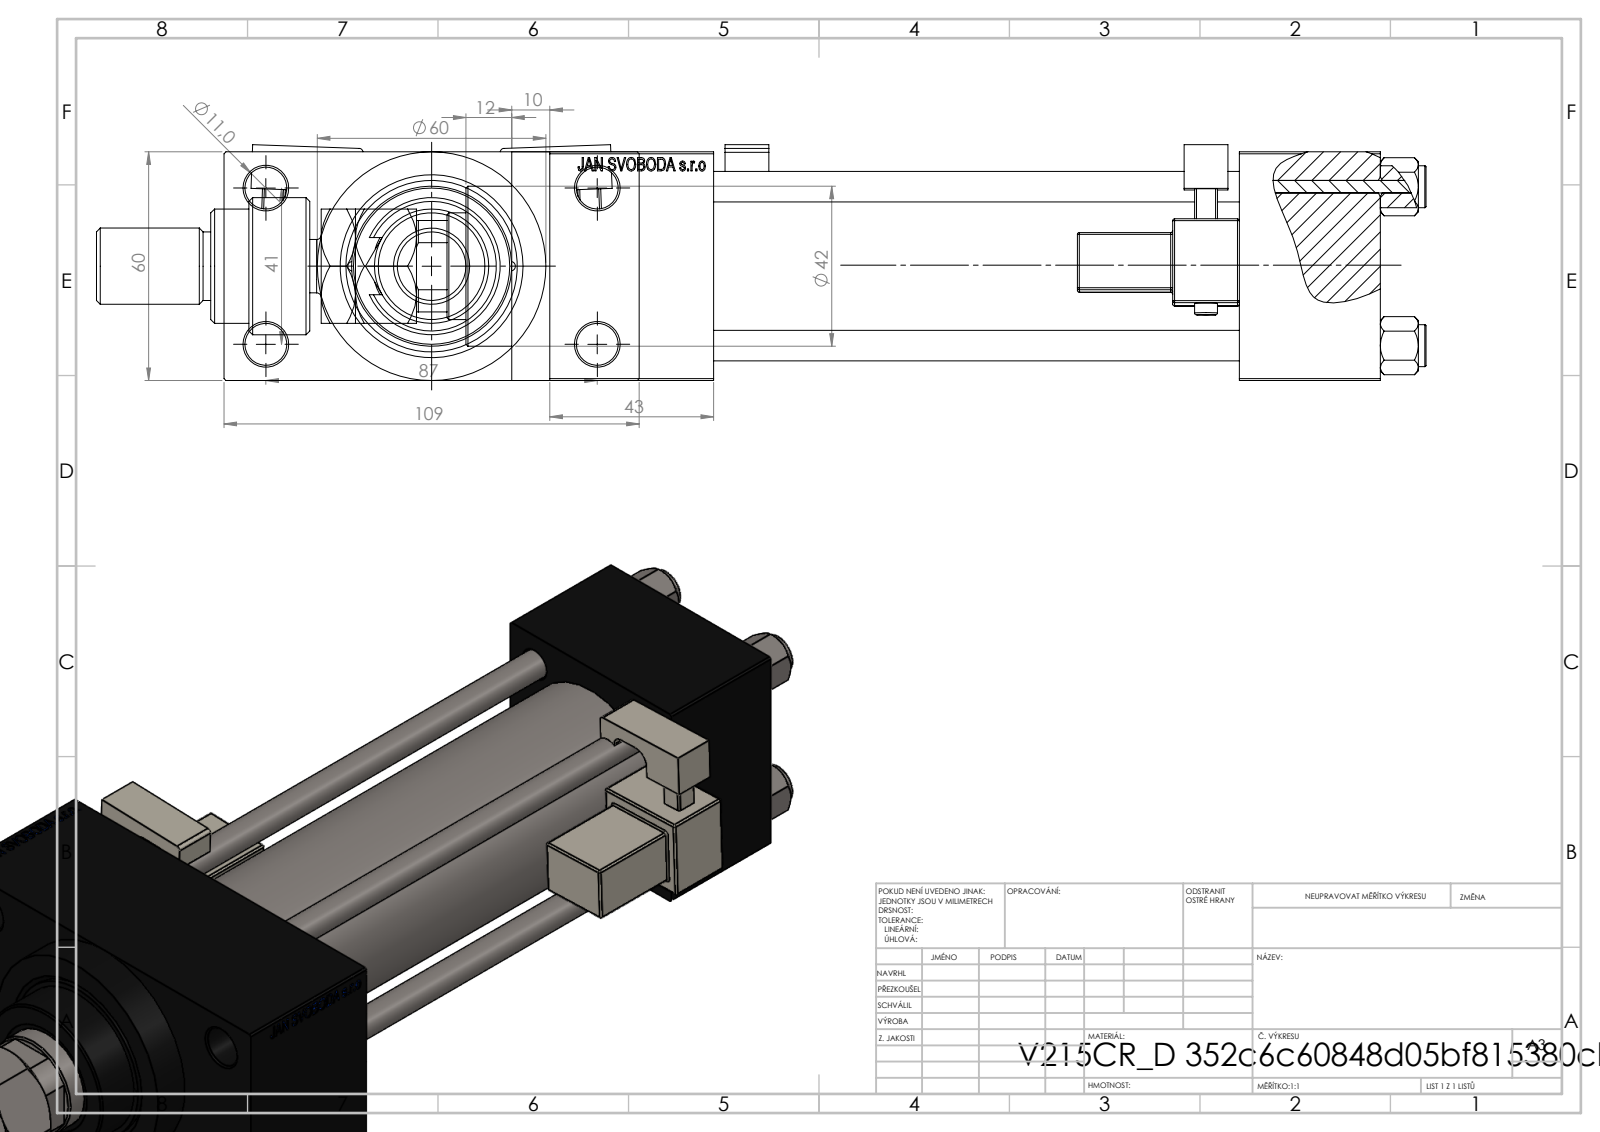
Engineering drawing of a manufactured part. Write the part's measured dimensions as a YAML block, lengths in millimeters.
part_name: "V215CR_D_TYCINKA; NUT_M5_D; FEMALE_PART_FOR_DFA; V215CR_MSU (+4 more)"
step_written_by: "SolidWorks 2019 (CONFIG_CONTROL_DESIGN)"
units: millimeters
bodies: {solids: 15, faces: 1353, planar: 588, cylindrical: 165, other: 600}
overall_size: [349, 109, 61.9]
volume: 716186
surface_area: 191099
round_holes:
  - {diameter: 8, count: 4}
  - {diameter: 11, count: 4}
  - {diameter: 2.5, count: 2}
  - {diameter: 7, count: 2}
  - {diameter: 16.66, count: 2}
  - {diameter: 24, count: 2}
  - {diameter: 18.5, count: 1}
  - {diameter: 28, count: 1}
  - {diameter: 31, count: 1}
  - {diameter: 40, count: 1}
  - {diameter: 45, count: 1}
round_bosses_or_shafts:
  - {diameter: 11, count: 4}
  - {diameter: 6, count: 2}
  - {diameter: 60, count: 1}
  - {diameter: 46, count: 1}
  - {diameter: 42, count: 1}
  - {diameter: 36, count: 1}
  - {diameter: 30, count: 1}
  - {diameter: 22, count: 1}
partial_cylinders:
  - {radius: 0.5, count: 48}
  - {radius: 1, count: 2}
  - {radius: 2.5, count: 2}
  - {radius: 4, count: 2}
  - {radius: 7.5, count: 1}
  - {radius: 12, count: 1}
  - {radius: 13.5, count: 1}
face_to_face_distances: [60, 138, 24.5, 84.5, 37, 175, 43, 218, 181, 109]
hole_center_spacings: [20.85, 22.65, 29.49, 30.62, 41.7, 46.53, 47.15, 48.09]
